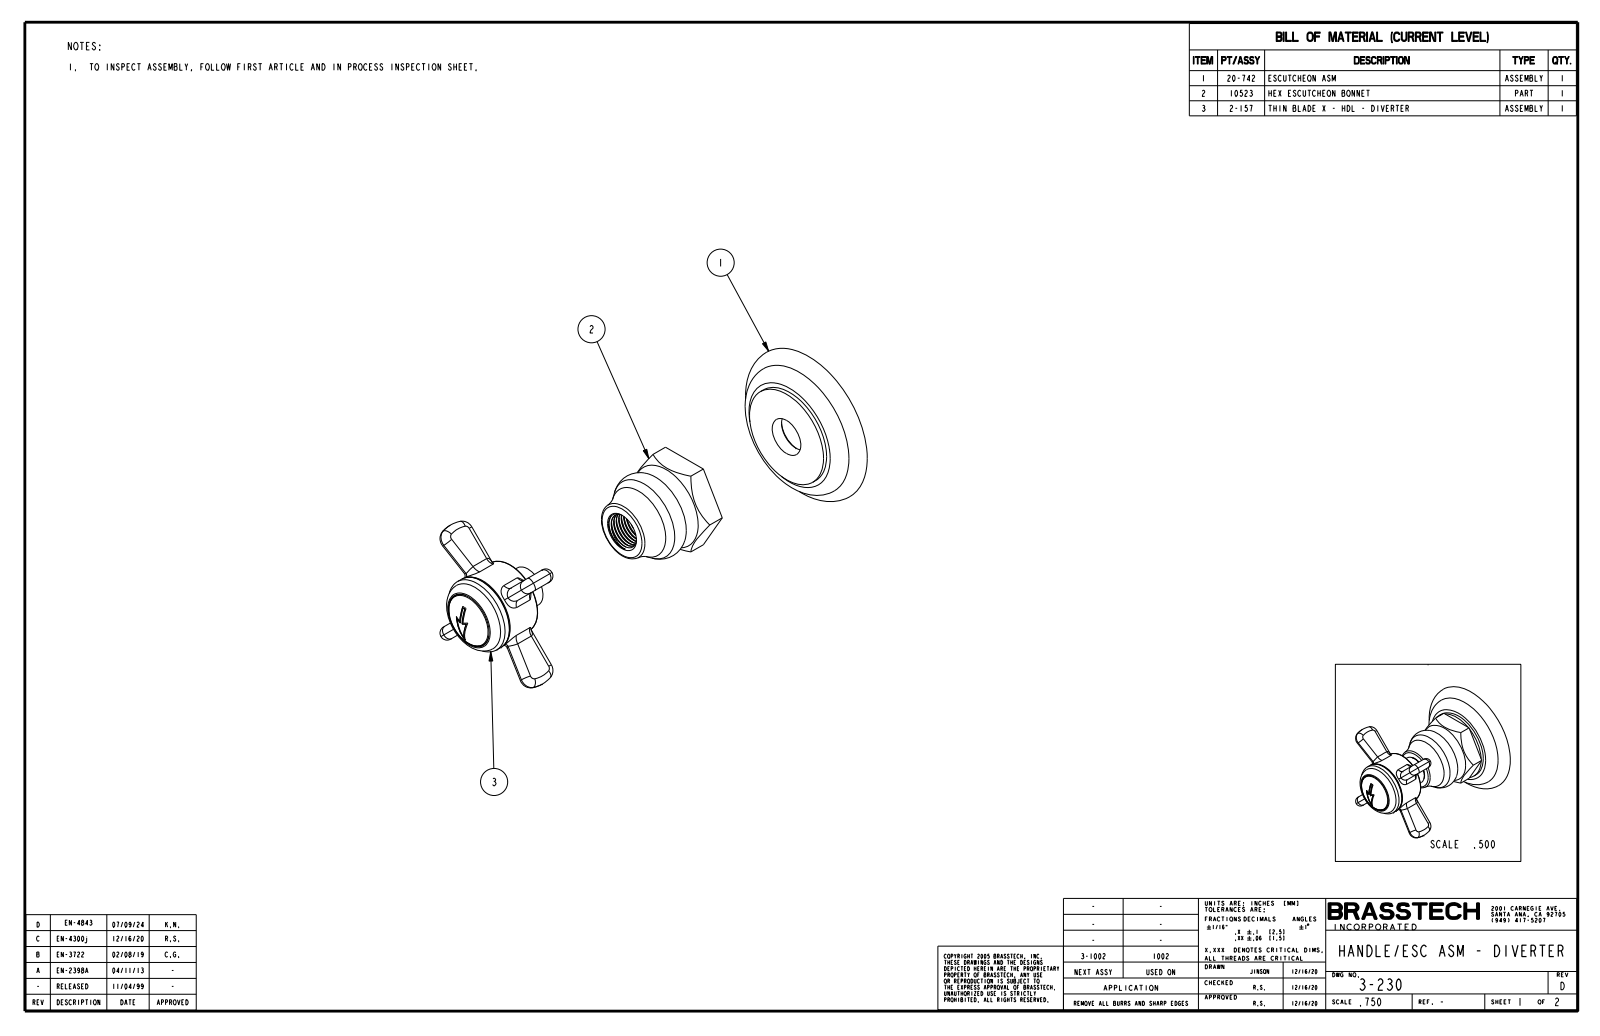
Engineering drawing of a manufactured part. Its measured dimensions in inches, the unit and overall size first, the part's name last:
Units: inches
Overall size (bounding box): 3.042 × 2.36 × 2.36
Round holes (diameter × count): ⌀0.815 ×1
Round bosses / shafts (diameter × count): ⌀1.482 ×1, ⌀1.115 ×1, ⌀1.1 ×1, ⌀0.8 ×1, ⌀0.603 ×1, ⌀0.4 ×1
Partial cylindrical surfaces — rounded edges, fillets, slot ends (radius × count): R0.1 ×14
Main face-to-face distances: 0.2, 2.057, 1.313, 1.687, 0.37, 0.375, 1.312, 1.682, 1.313, 0.437
Volume: 4.027 in³ · Surface area: 23.32 in²
Bodies: 1 solid, 170 faces (46 planar, 30 cylindrical, 94 other)
Part name (STEP PRODUCT): 3-230
STEP written by: CREO PARAMETRIC BY PTC INC, 2018400 (CONFIG_CONTROL_DESIGN)
